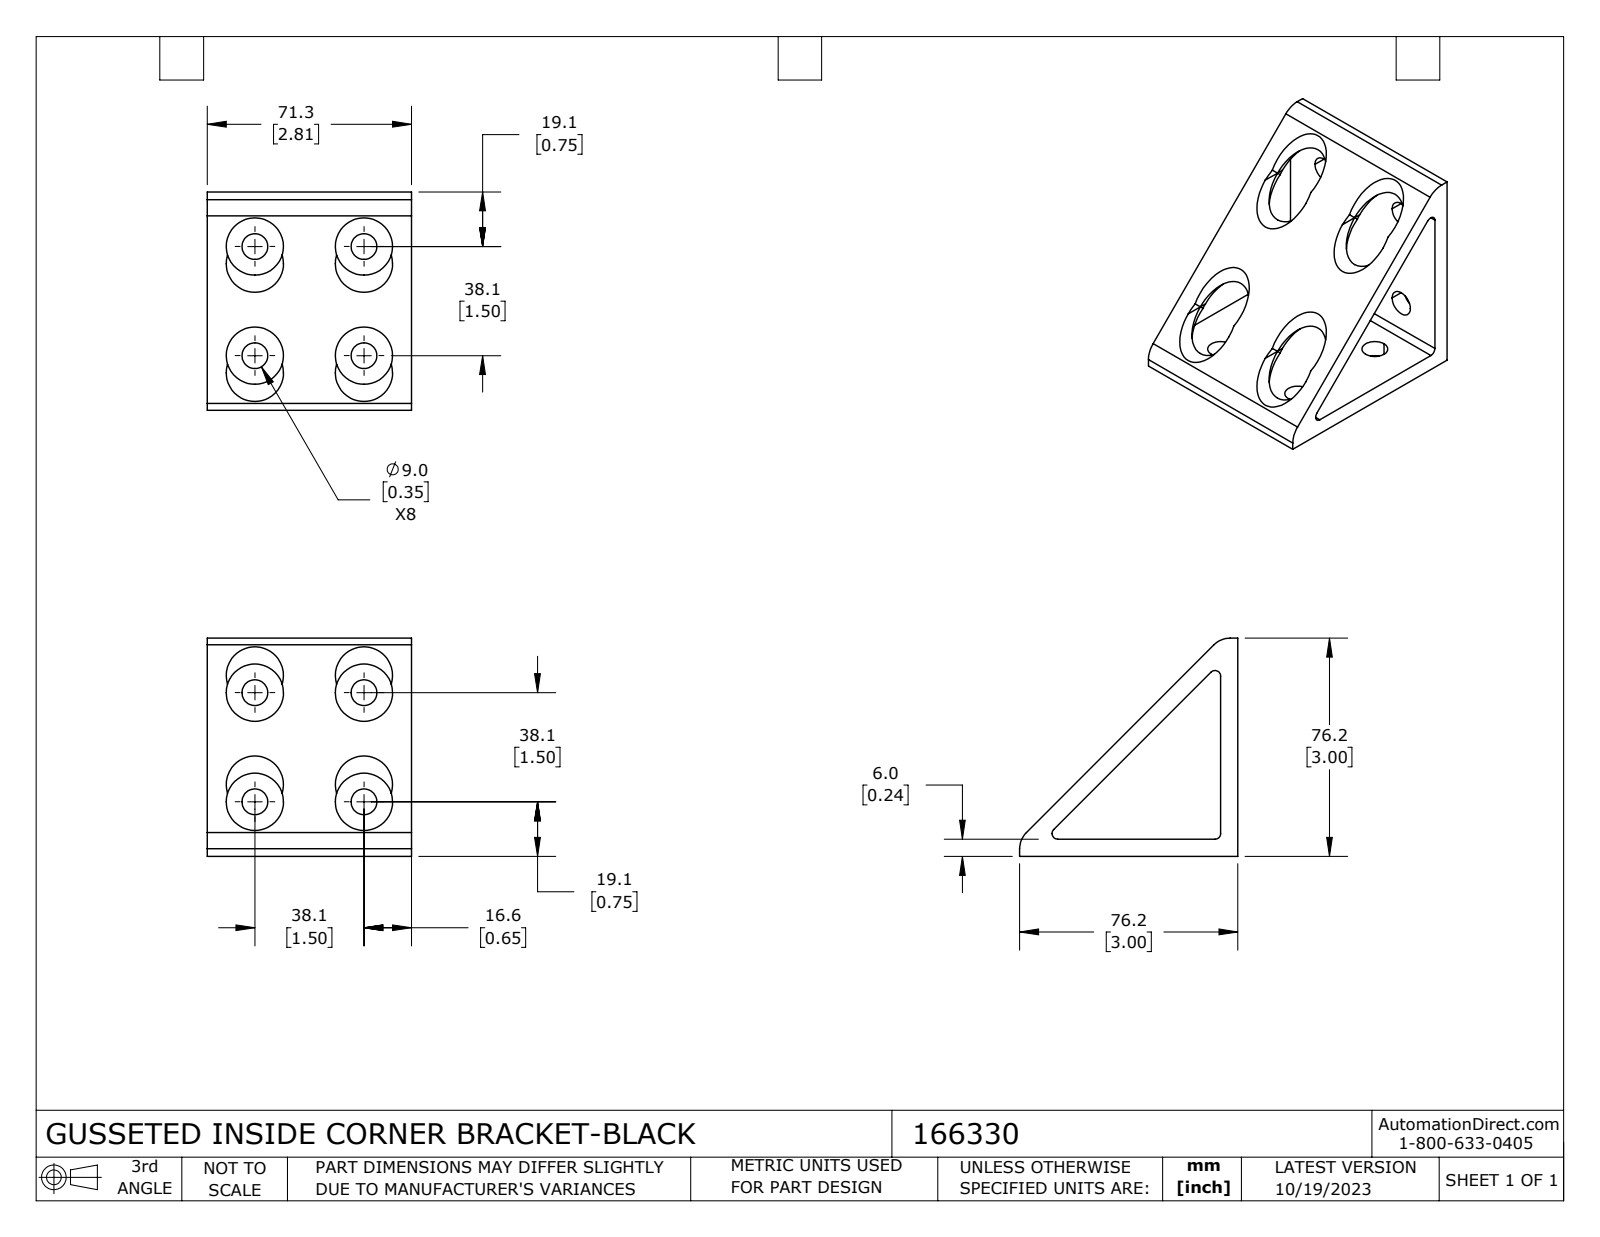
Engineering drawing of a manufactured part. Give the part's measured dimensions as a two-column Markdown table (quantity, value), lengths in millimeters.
| quantity | value |
| --- | --- |
| part name | 166330 |
| STEP written by | SolidWorks 2023 (CONFIG_CONTROL_DESIGN) |
| units | millimeters |
| bodies | 1 solid, 74 faces (10 planar, 64 cylindrical, 0 other) |
| overall size | 76.2 × 76.2 × 71.3 |
| volume | 87 455 mm³ |
| surface area | 34 201 mm² |
| round holes (diameter × count) | 9 × 8, 20 × 8 |
| partial cylindrical surfaces (radius × count) | 2 × 3, 8 × 2 |
| main face-to-face distances | 6, 71.3, 76.2, 70.2 |
| hole center spacings | 38.1, 53.88 |
